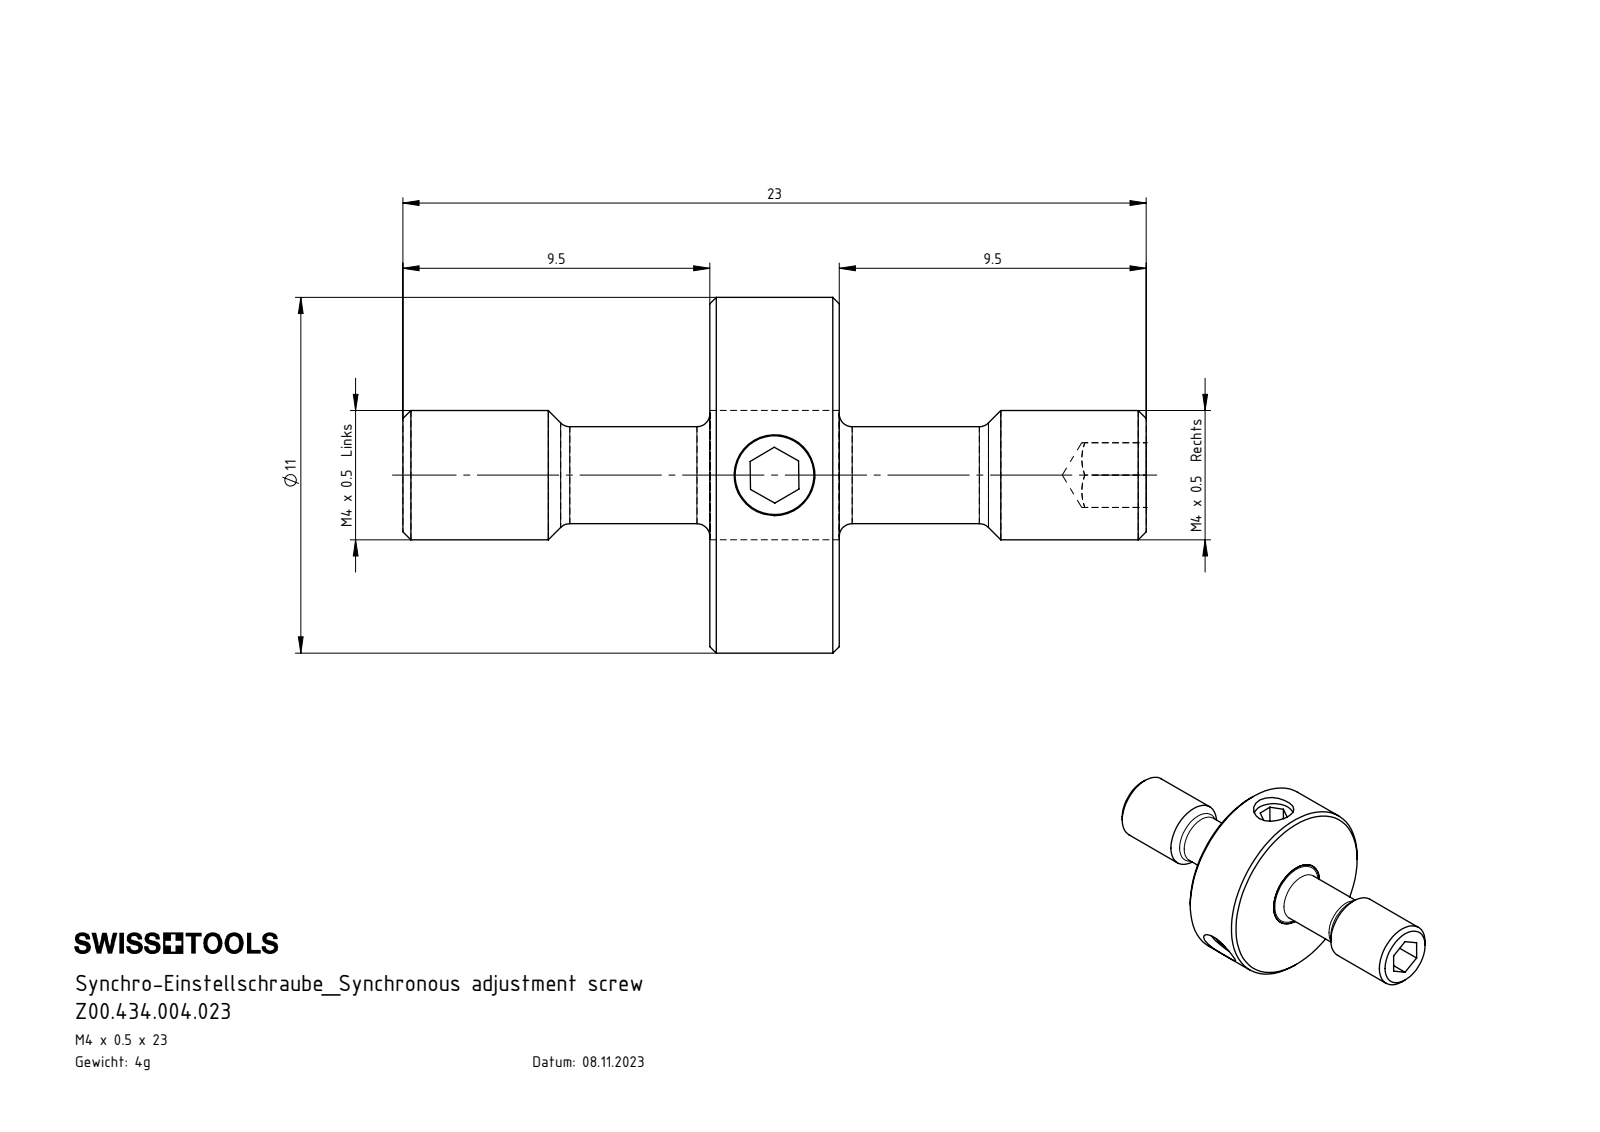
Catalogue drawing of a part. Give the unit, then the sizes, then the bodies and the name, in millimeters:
Units: millimetres
Overall size (bounding box): 23 × 11 × 11
Round holes (diameter × count): ⌀2.5 ×3
Round bosses / shafts (diameter × count): ⌀3 ×4, ⌀11 ×1, ⌀4 ×1
Main face-to-face distances: 4, 9.5, 13.5, 1.5, 2, 3, 10.75, 12.25, 1.25, 2.75
Volume: 553 mm³ · Surface area: 853 mm²
Bodies: 5 solids, 99 faces (39 planar, 26 cylindrical, 34 other)
Part name (STEP PRODUCT): ISO 4026 - M3 x 3; Z25-ER3.002.004_A; Z00.434.004.023; Z25-ER3.001.023_A
STEP written by: SolidWorks 2022 (AUTOMOTIVE_DESIGN)
